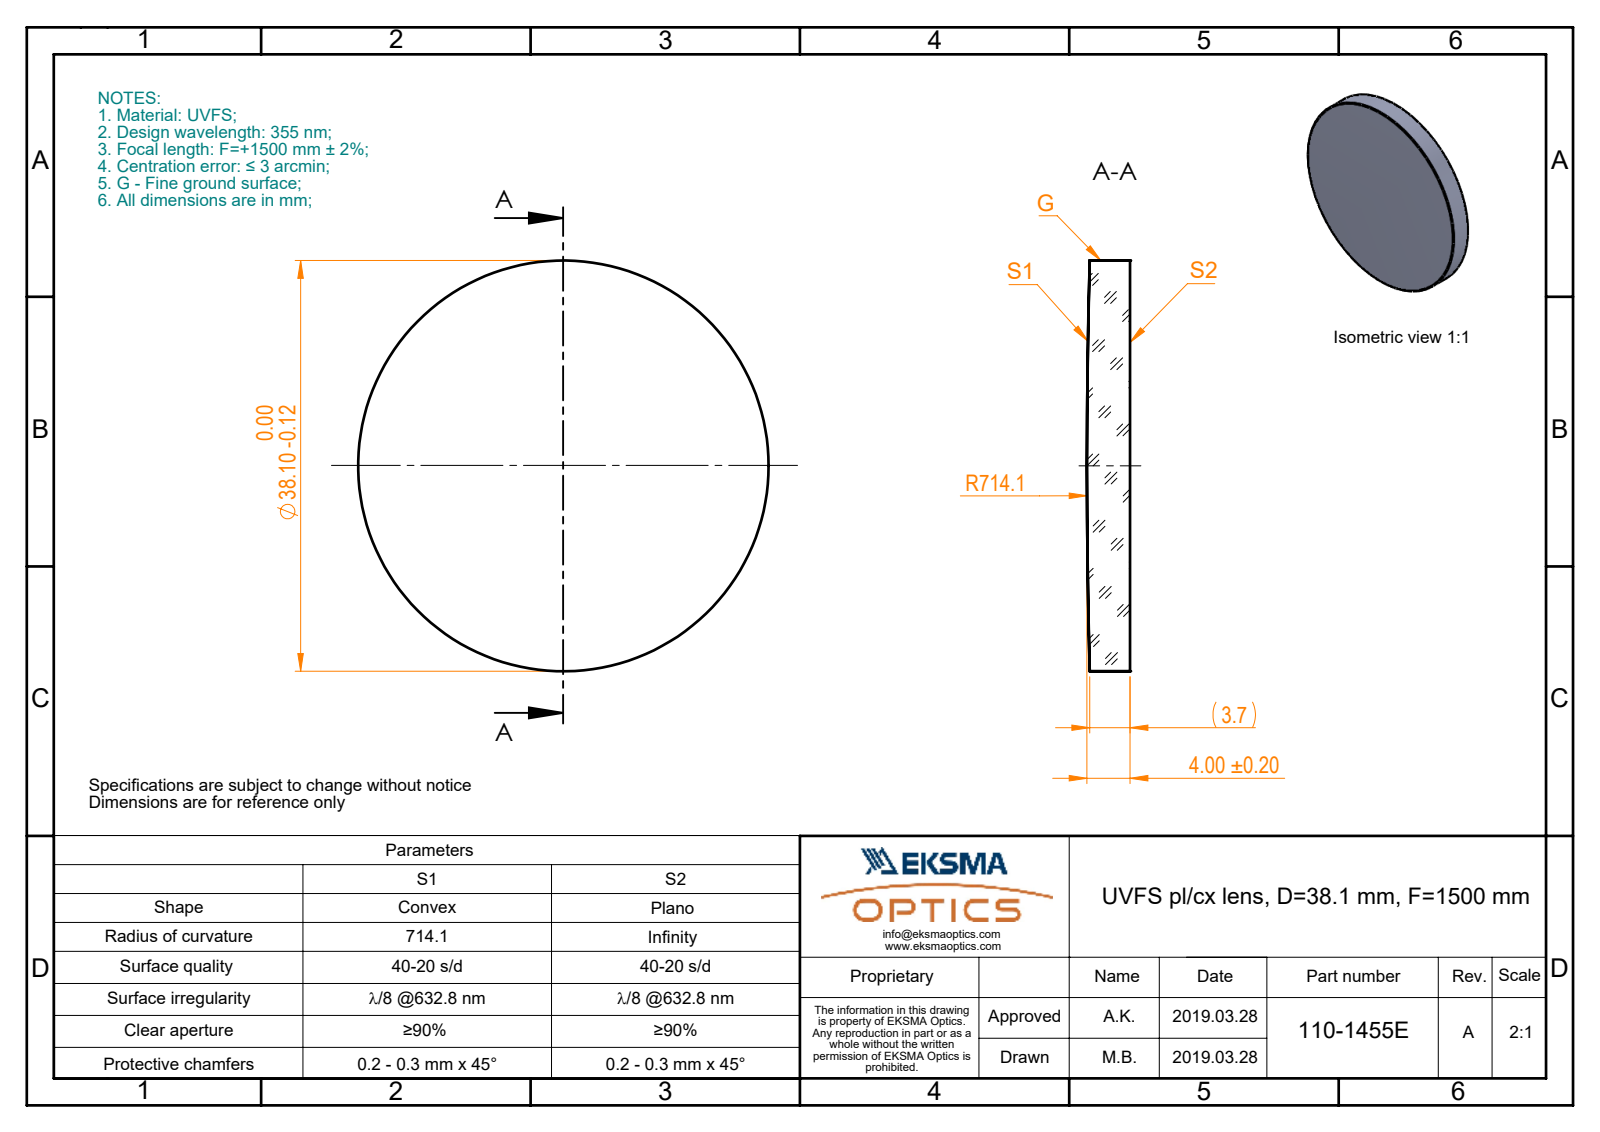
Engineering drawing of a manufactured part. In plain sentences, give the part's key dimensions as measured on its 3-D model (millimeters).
The part is named "110-1455E UVFS pl-cx 38.1 F1500". Its 3-D file was written by "SolidWorks 2017 (CONFIG_CONTROL_DESIGN)". It is 1 solid with 5 faces: 1 planar, 2 cylindrical and 2 other. Overall it measures 38.1 by 38.1 by 4 millimeters. Its volume is 4 416 cubic millimeters and its surface area 2 729 square millimeters. Round bosses or shafts: 1 of diameter 38.1.
